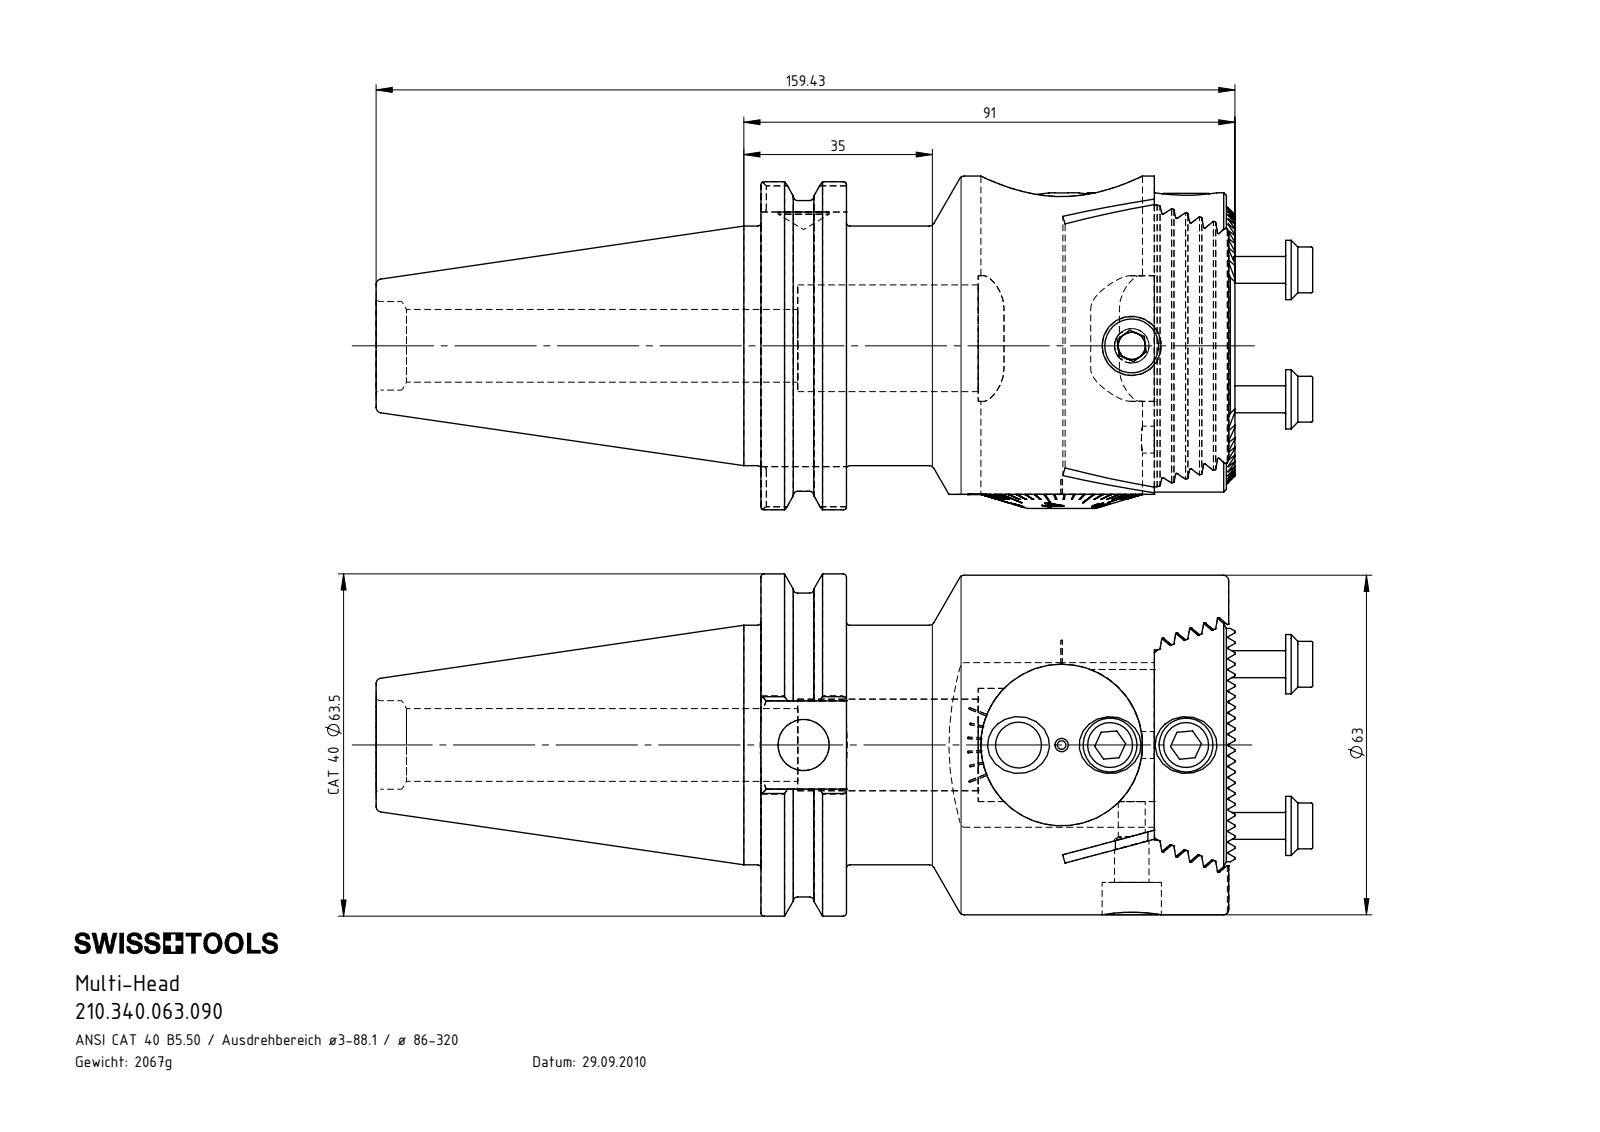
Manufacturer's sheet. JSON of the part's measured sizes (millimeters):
{"part_name": "A55-BG2.013.005_C; ISO 4026 - M10 x 16; ISO 4026 - M8 x 6; MH1-BG1.001.049 (+8 more)", "step_written_by": "SolidWorks 2022 (CONFIG_CONTROL_DESIGN)", "units": "millimeters", "bodies": {"solids": 19, "faces": 1215, "planar": 609, "cylindrical": 268, "other": 338}, "overall_size": [173.85, 63.5, 61.91], "volume_mm3": 263332, "surface_area_mm2": 76944, "round_holes": [[4.2, 5], [8.5, 4], [6.8, 3], [11, 3], [5, 2], [20, 2], [1, 1], [1.6, 1], [3.3, 1], [6.4, 1], [8, 1], [9.5, 1]], "round_bosses_or_shafts": [[11, 4], [8.5, 4], [5, 4], [10, 3], [63.5, 1], [63, 1], [56.36, 1], [44.45, 1]], "partial_cylinders_radius": [[0.14, 21], [0.2, 20], [0.8, 8], [6, 6], [4, 2], [8.5, 2], [31, 2], [2, 1]], "face_to_face_distances": [2.38, 7.15, 57.15, 1.73, 15.87, 73.02, 4.76, 8.66, 5.2, 4.77], "hole_center_spacings": [16.73, 16.77, 17.4, 17.97, 18.03, 20.52, 20.59, 24]}
